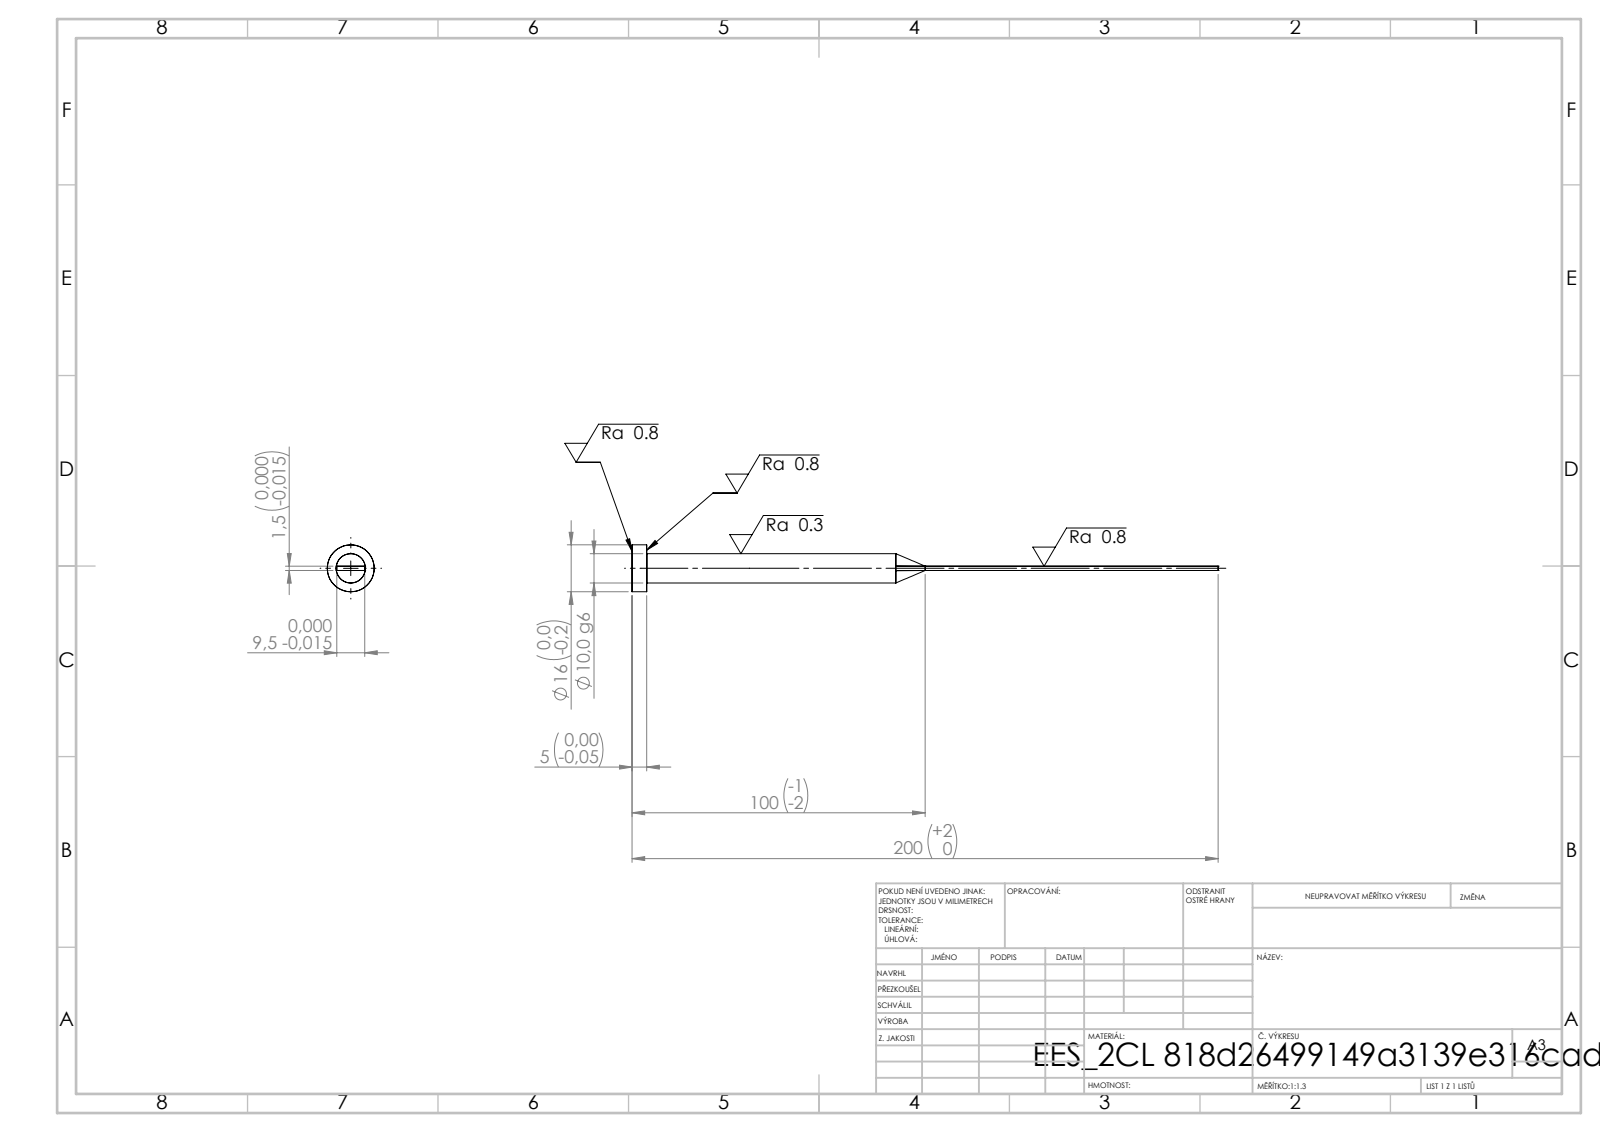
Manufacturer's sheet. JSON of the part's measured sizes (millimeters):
{"step_written_by": "SolidWorks 2019 (CONFIG_CONTROL_DESIGN)", "units": "millimeters", "bodies": {"solids": 1, "faces": 15, "planar": 7, "cylindrical": 4, "other": 4}, "overall_size": [200, 16, 16], "volume_mm3": 9544, "surface_area_mm2": 5724, "round_bosses_or_shafts": [[16, 1], [10, 1]], "face_to_face_distances": [1.5, 9.5, 5, 200, 195]}
